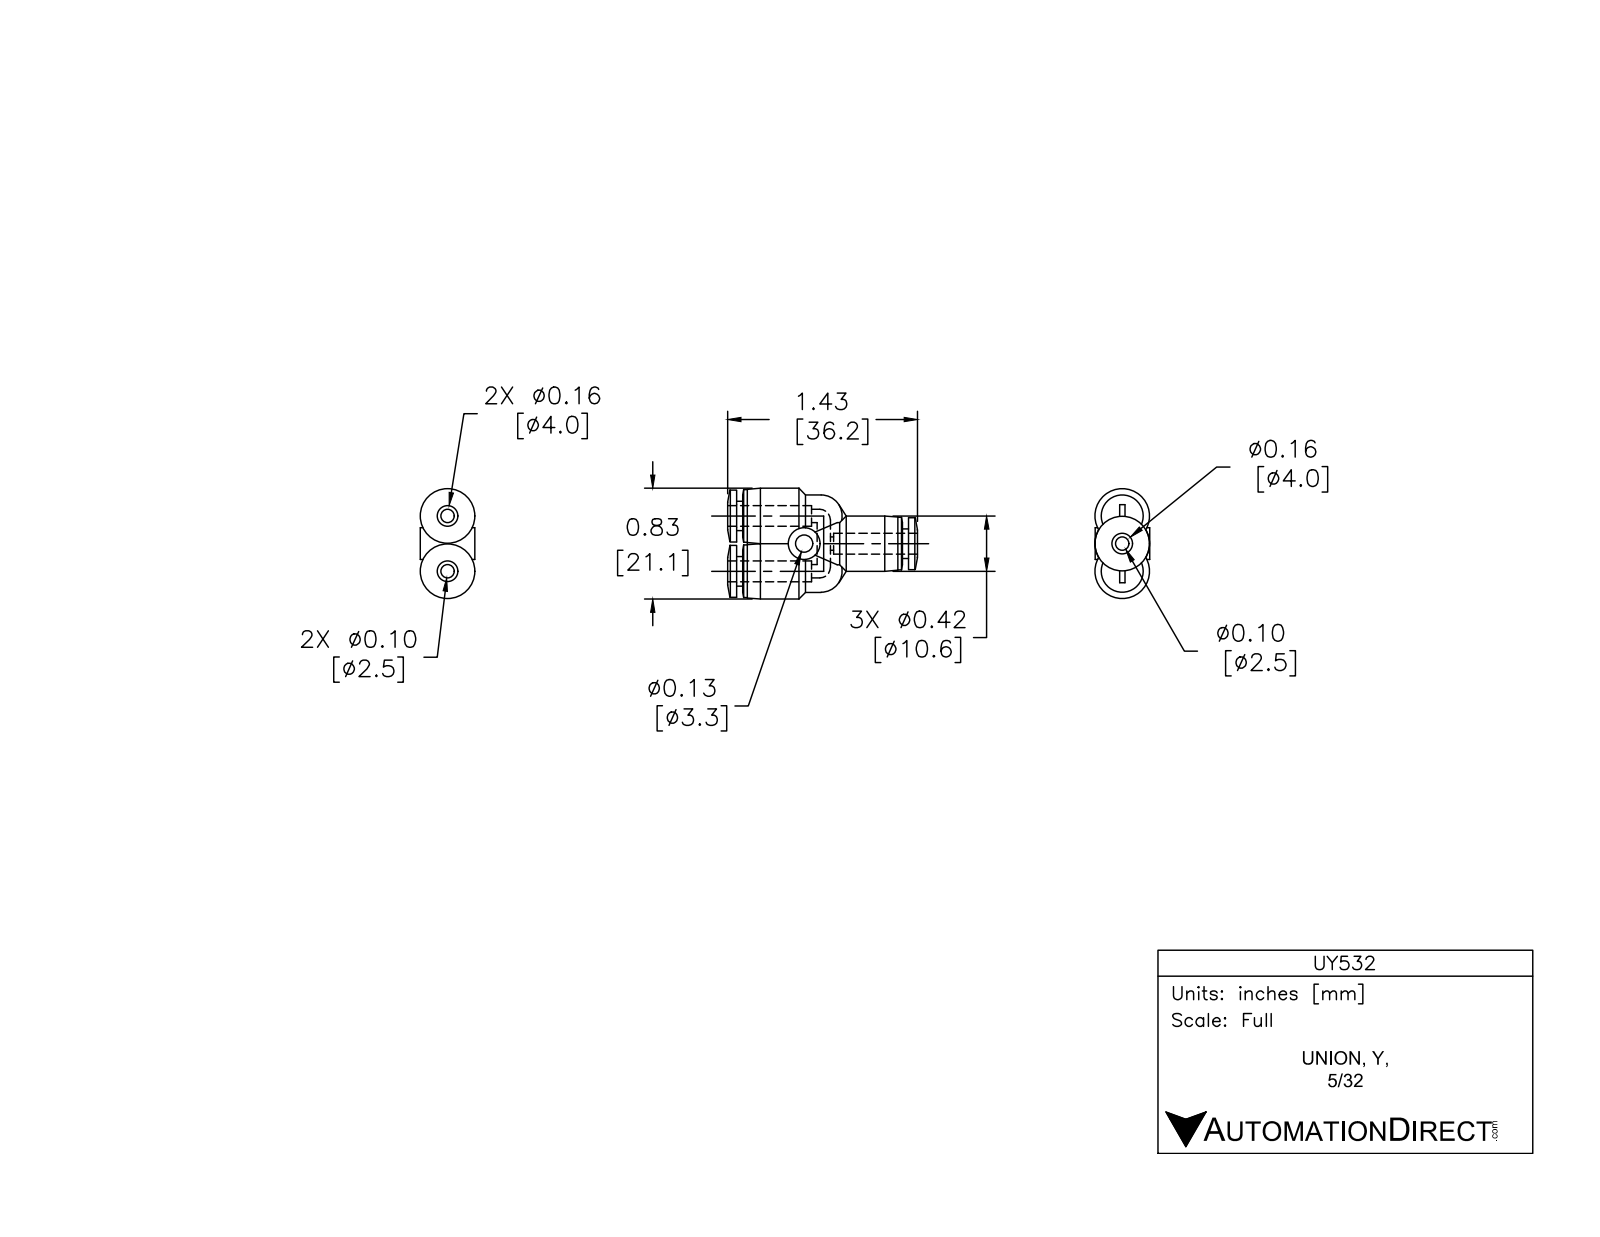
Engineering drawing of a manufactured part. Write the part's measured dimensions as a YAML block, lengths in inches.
part_name: "UY532"
step_written_by: "SolidWorks 2015 (AUTOMOTIVE_DESIGN)"
units: inches
bodies: {solids: 1, faces: 109, planar: 19, cylindrical: 40, other: 50}
overall_size: [1.417, 0.827, 0.413]
volume: 0.211
surface_area: 4.726
round_holes:
  - {diameter: 0.169, count: 3}
  - {diameter: 0.13, count: 1}
round_bosses_or_shafts:
  - {diameter: 0.413, count: 3}
  - {diameter: 0.394, count: 3}
  - {diameter: 0.388, count: 3}
  - {diameter: 0.22, count: 3}
  - {diameter: 0.236, count: 1}
partial_cylinders:
  - {radius: 0.157, count: 3}
face_to_face_distances: [0.045, 1.238, 1.283, 1.193, 0.563, 0.72, 0.518, 0.675, 0.413, 0.079]
hole_center_spacings: [0.207, 0.413]
